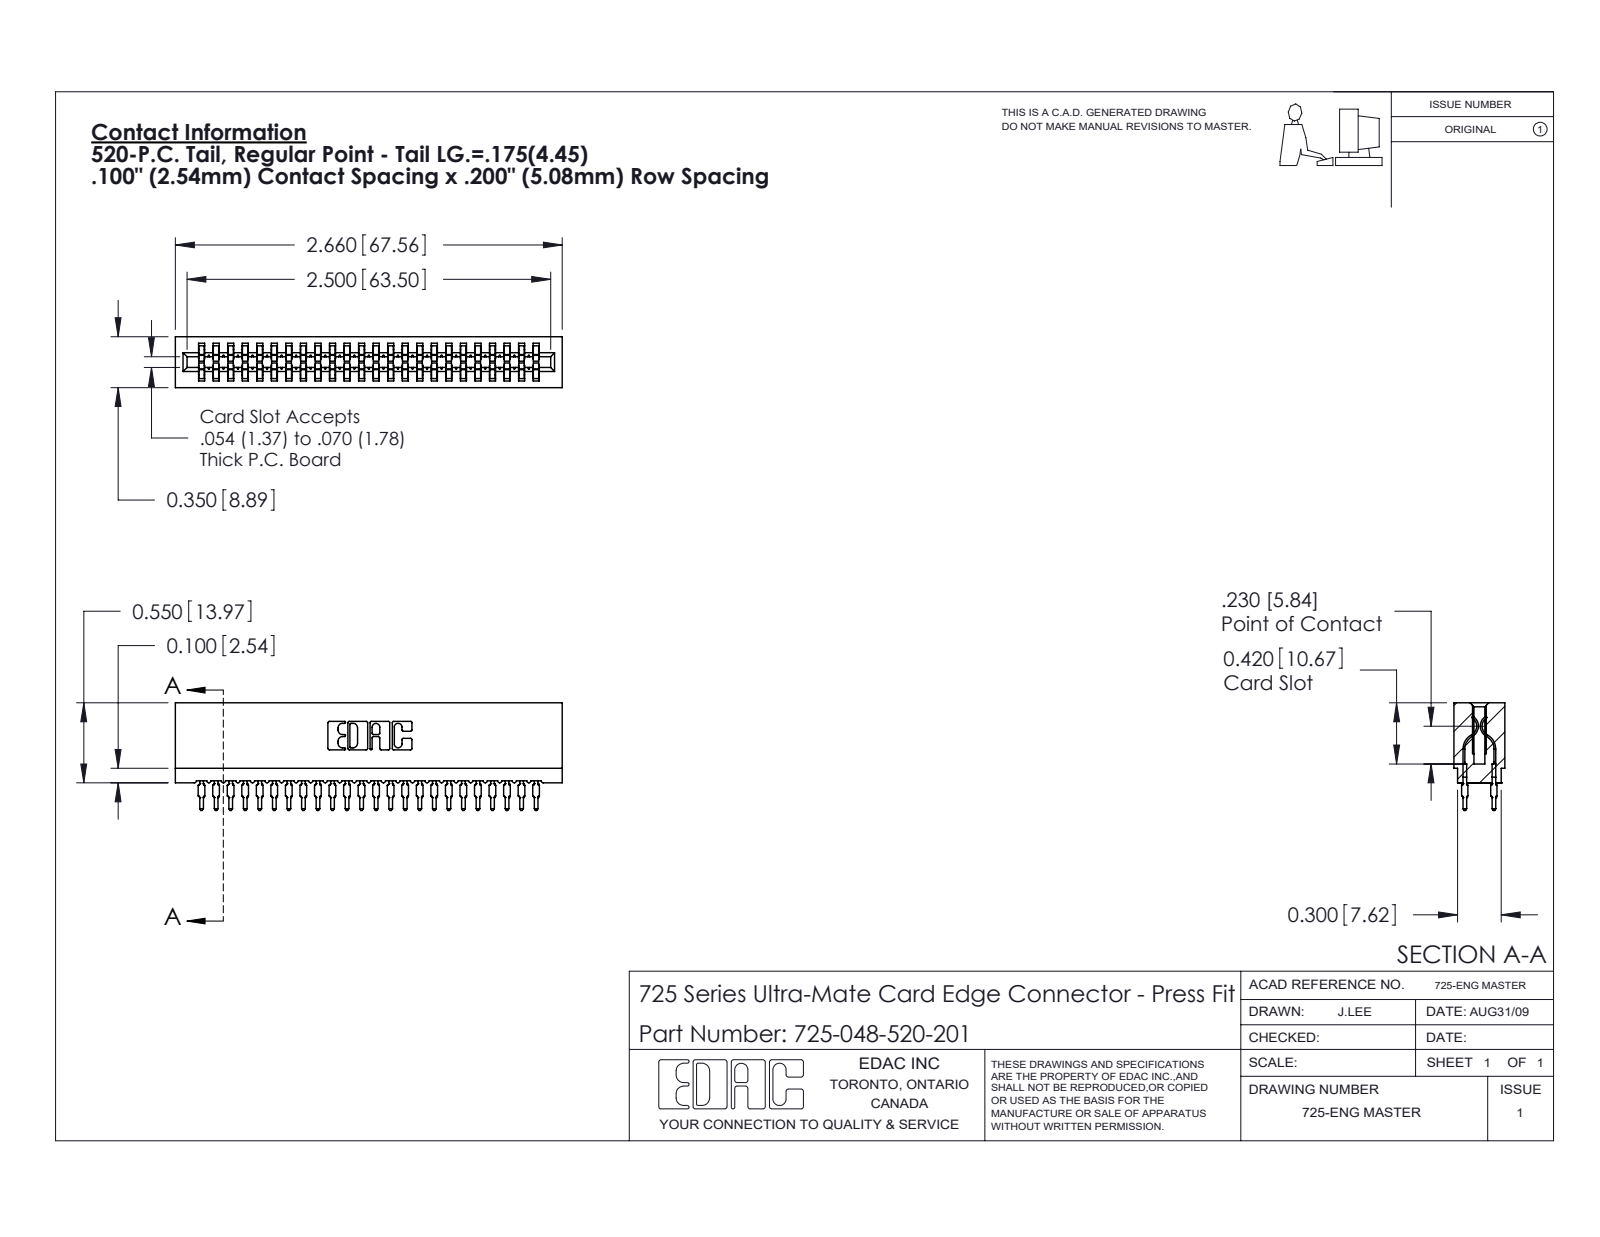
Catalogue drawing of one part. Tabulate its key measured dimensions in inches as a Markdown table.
| quantity | value |
| --- | --- |
| part name | 745-292-001_520; 725-048-520-201; 725 Part_Insulator Option - 01 |
| STEP written by | SolidWorks 2020 (CONFIG_CONTROL_DESIGN) |
| units | inches |
| bodies | 49 solids, 4391 faces (2263 planar, 880 cylindrical, 1248 other) |
| overall size | 2.66 × 0.741 × 0.35 |
| volume | 0.33 in³ |
| surface area | 16.79 in² |
| partial cylindrical surfaces (radius × count) | 0.021 × 96, 0.015 × 48, 0.01 × 22, 0.005 × 8, 0.011 × 8, 0.007 × 6, 0.031 × 6, 0.026 × 3 |
| main face-to-face distances | 0.2, 0.1, 0.3, 0.4, 0.5, 0.35, 0.6, 0.063, 0.287, 0.7 |
